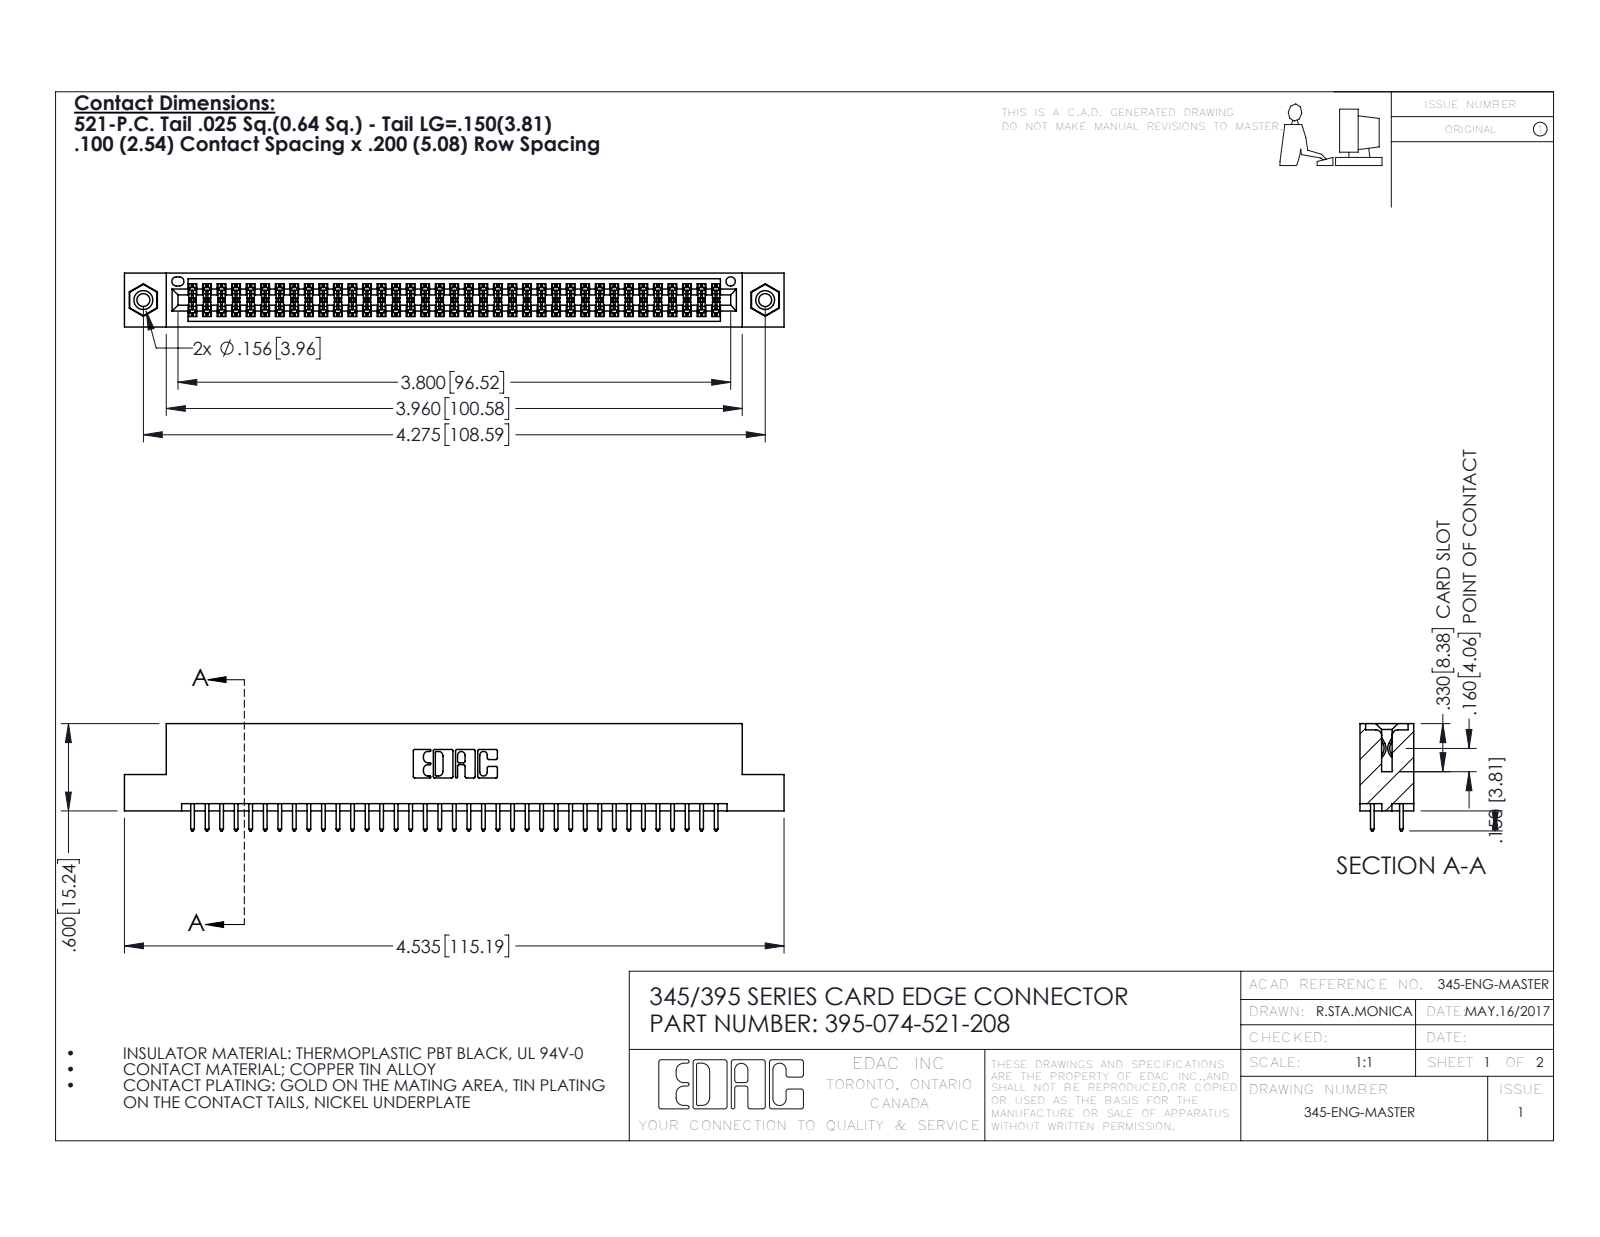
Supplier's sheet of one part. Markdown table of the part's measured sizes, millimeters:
| quantity | value |
| --- | --- |
| part name | 345-250-001_345-250-003-102; 395-074-521-208; 345-292-001_345-293-121; 345 Part_Flush Mounting Lugs - 0.156 Dia-TI |
| STEP written by | SolidWorks 2016 (CONFIG_CONTROL_DESIGN) |
| units | millimeters |
| bodies | 77 solids, 3886 faces (2554 planar, 1316 cylindrical, 16 other) |
| overall size | 115.2 × 18.7 × 9.4 |
| volume | 11 100 mm³ |
| surface area | 16 140 mm² |
| round holes (diameter × count) | 2.3 × 2, 3.2 × 2, 4 × 2, 1.6 × 1 |
| round bosses / shafts (diameter × count) | 3.9 × 2 |
| partial cylindrical surfaces (radius × count) | 0.2 × 111, 0.3 × 74, 0.3 × 22, 0.2 × 6, 0.8 × 6, 0.7 × 3, 0.4 × 2, 0.5 × 2 |
| main face-to-face distances | 1.8, 7.6, 5.1, 9.4, 2.5, 6.9, 0.6, 5.7, 4.4, 3.8 |
| hole center spacings | 6.9, 102.6, 108.6 |
